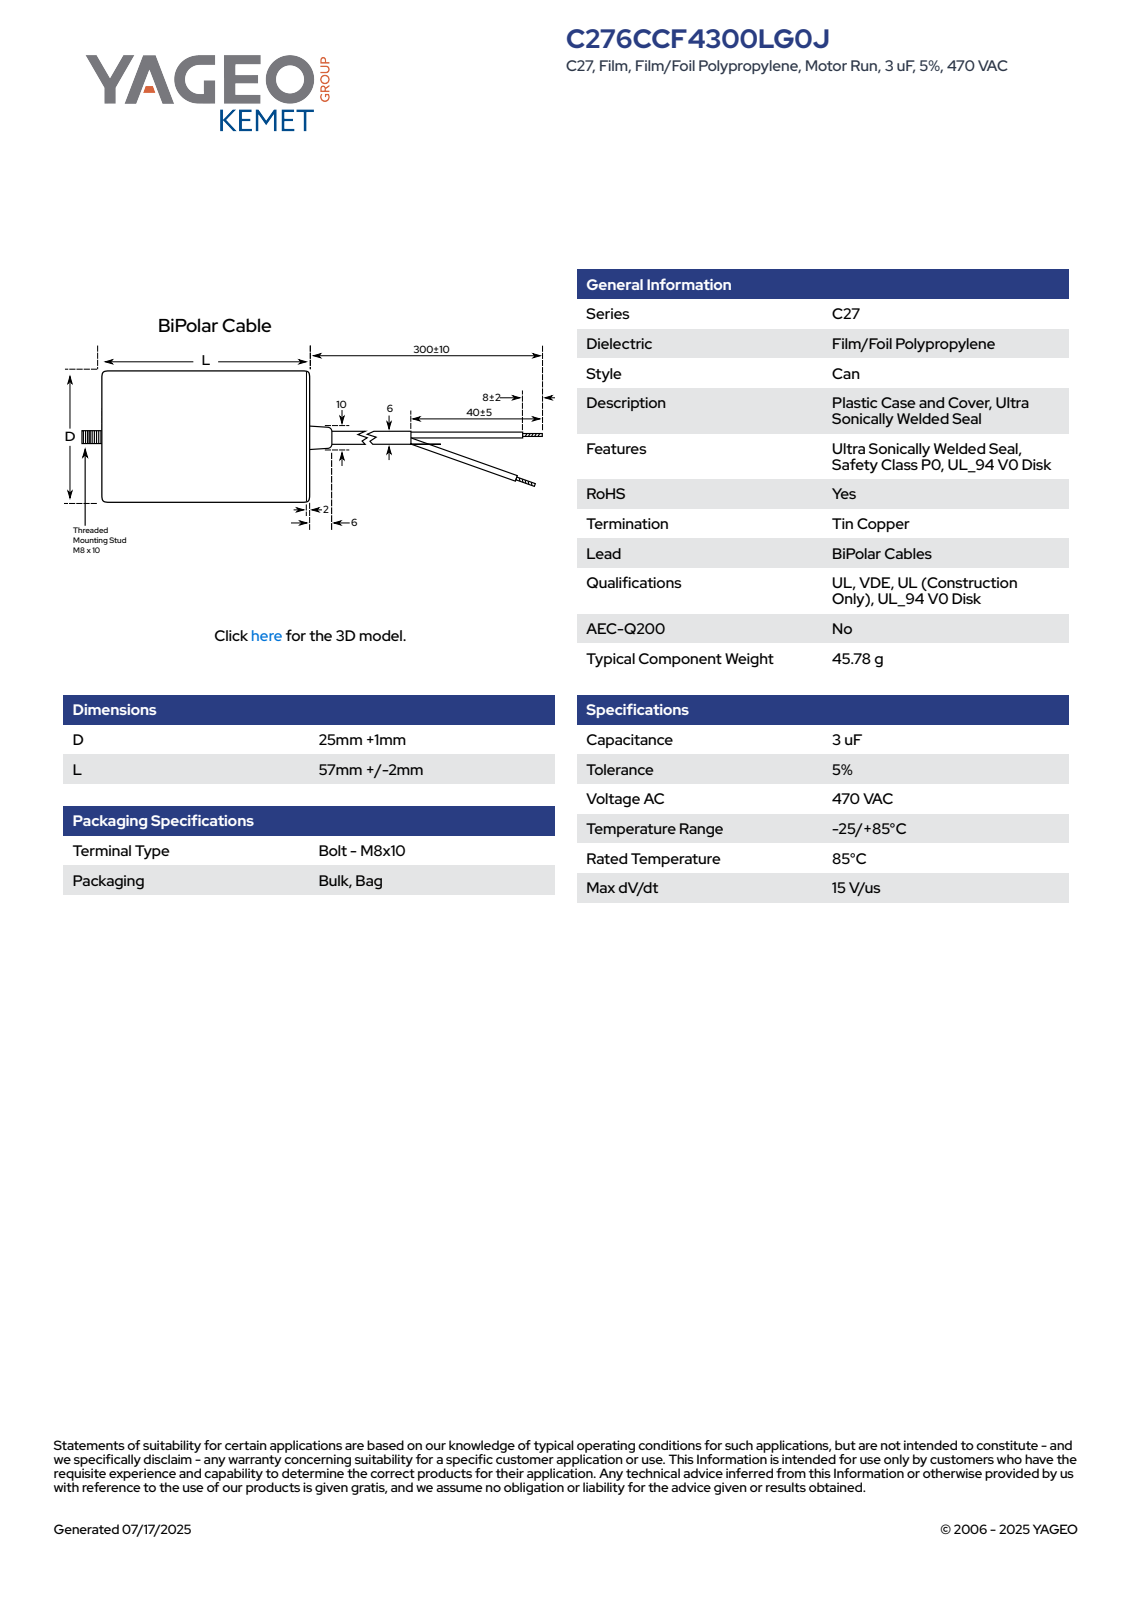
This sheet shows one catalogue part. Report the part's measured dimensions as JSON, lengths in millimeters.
{"part_name": "CFM_KC27BI_25X57_D26L59", "step_written_by": "SolidWorks 2014 (AUTOMOTIVE_DESIGN)", "units": "millimeters", "bodies": {"solids": 2, "faces": 82, "planar": 28, "cylindrical": 15, "other": 39}, "overall_size": [75, 26.01, 26], "volume_mm3": 31414, "surface_area_mm2": 6495, "round_holes": [[22, 1]], "round_bosses_or_shafts": [[26, 1], [8, 1]], "partial_cylinders_radius": [[13.01, 1]], "face_to_face_distances": [57, 59, 2, 10, 67, 69, 75, 65, 8, 6]}
